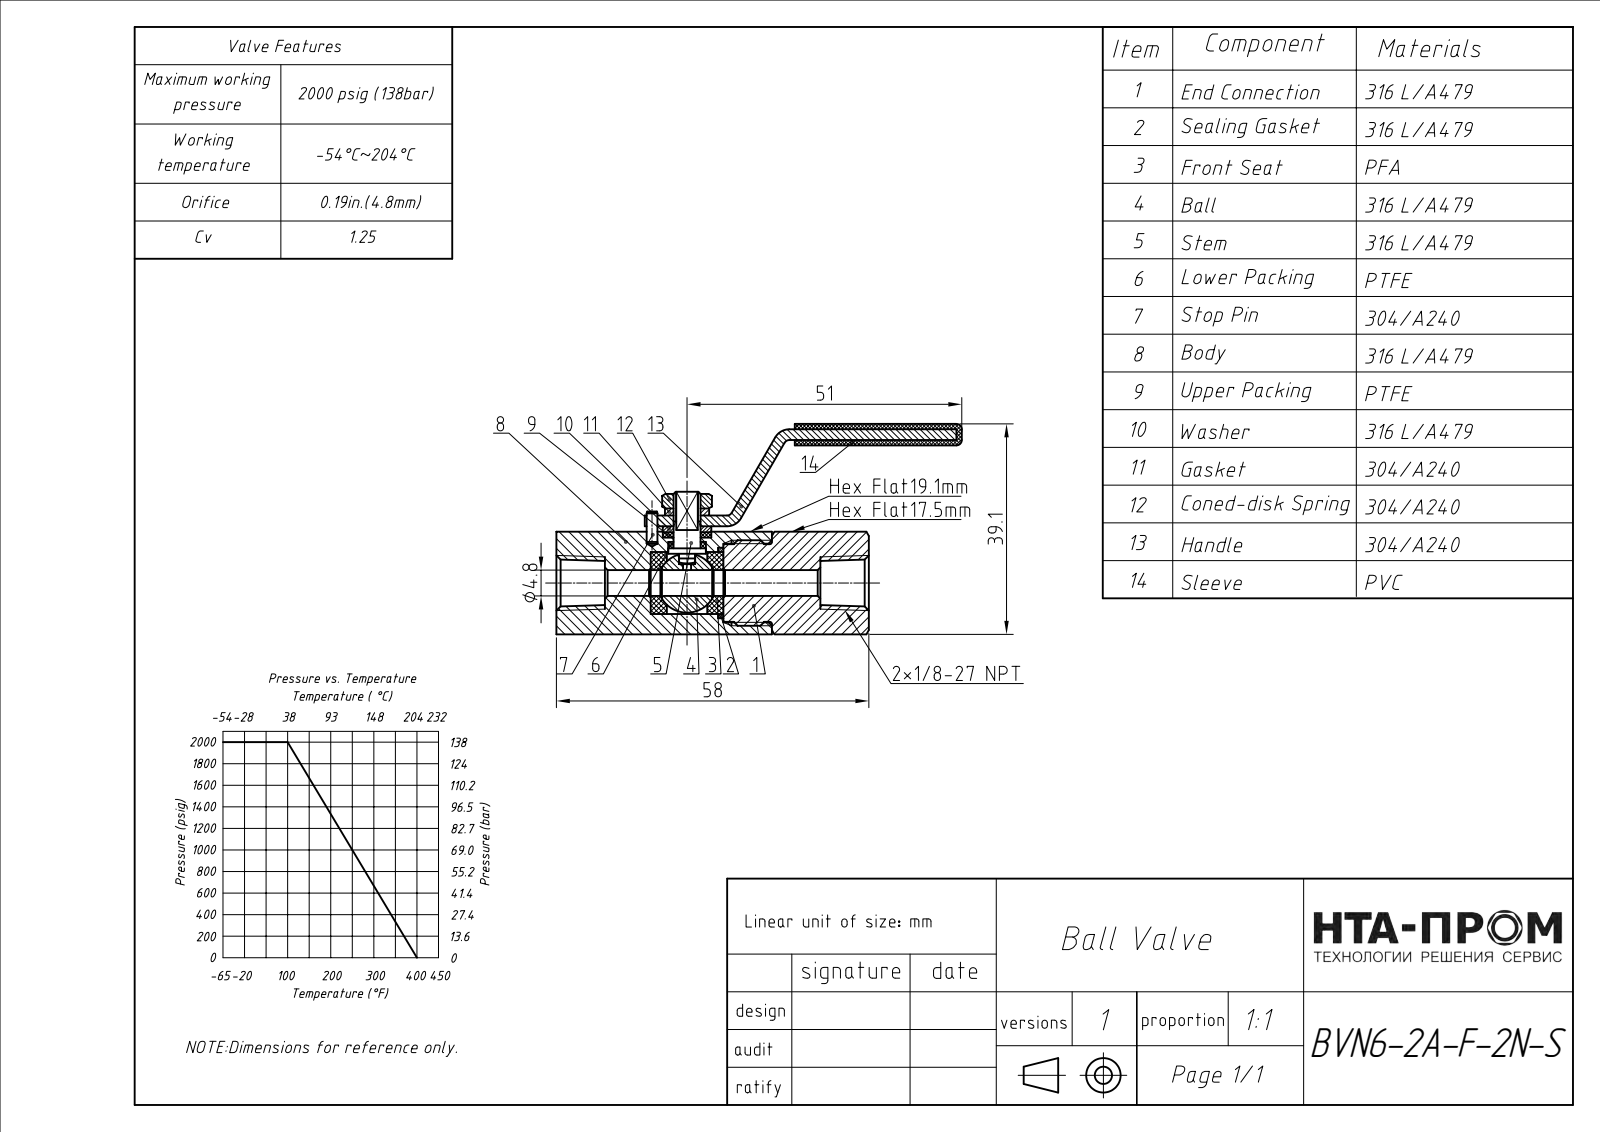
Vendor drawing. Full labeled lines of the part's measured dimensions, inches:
Part name (STEP PRODUCT): BVN6-2A-F-2N-S; BVN6; COMPOUND
STEP written by: FreeCAD (AUTOMOTIVE_DESIGN)
Units: inches
Bodies: 5 solids, 124 faces (55 planar, 39 cylindrical, 30 other)
Overall size (bounding box): 2.917 × 1.495 × 0.868
Volume: 1.068 in³ · Surface area: 15.01 in²
Round holes (diameter × count): ⌀0.189 ×1, ⌀0.453 ×1, ⌀0.575 ×1
Round bosses / shafts (diameter × count): ⌀0.625 ×1, ⌀0.567 ×1, ⌀0.323 ×1, ⌀0.276 ×1, ⌀0.197 ×1
Partial cylindrical surfaces — rounded edges, fillets, slot ends (radius × count): R0.024 ×4, R0.039 ×4, R0.197 ×3, R0.02 ×2, R0.079 ×2, R0.118 ×2, R0.315 ×1, R0.375 ×1
Main face-to-face distances: 0.752, 0.079, 0.689, 1.495, 0.743, 1.417, 0.665, 0.709, 0.63, 1.22
